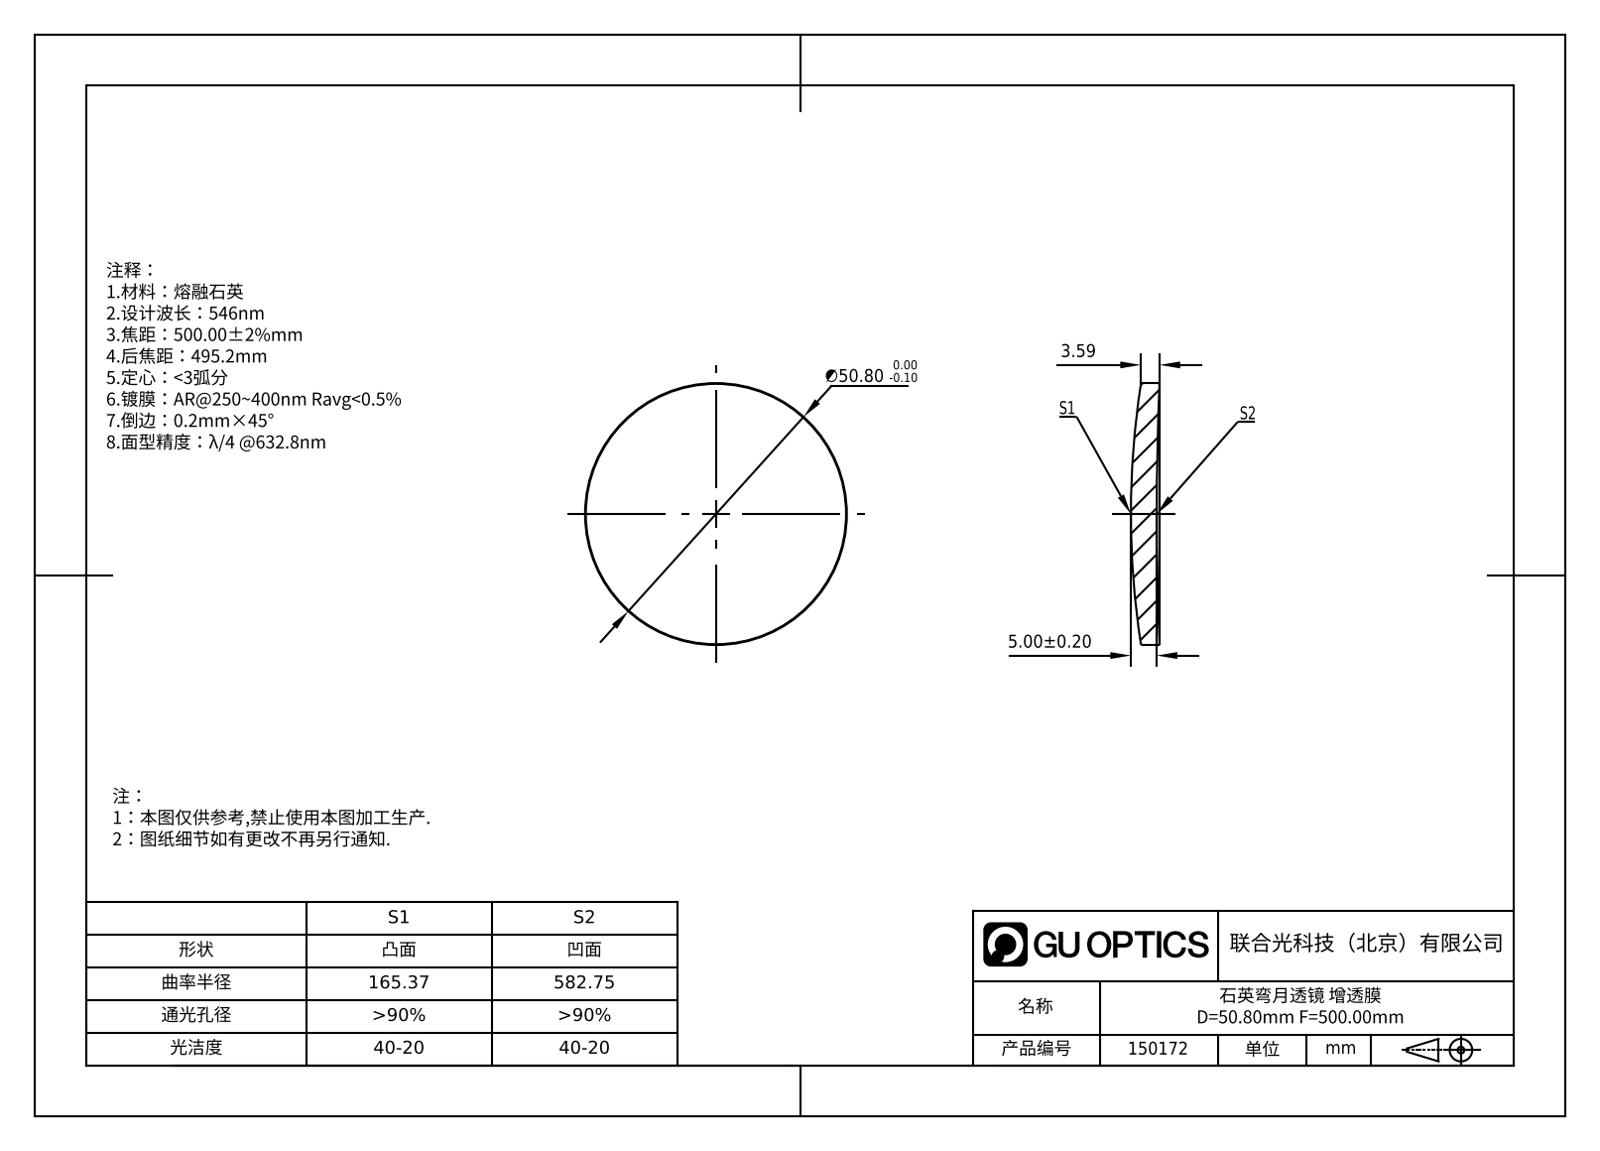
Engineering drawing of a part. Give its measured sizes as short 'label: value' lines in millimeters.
name: GLM2-050B-500-UV
written by: SolidWorks 2022 (AUTOMOTIVE_DESIGN)
unit: mm
bodies: 1 solid, 10 faces (0 planar, 2 cylindrical, 8 other)
size: 50.8 × 50.8 × 5.55
volume: 8 721 mm³; area: 4 605 mm²
bosses: 1× ⌀50.8
